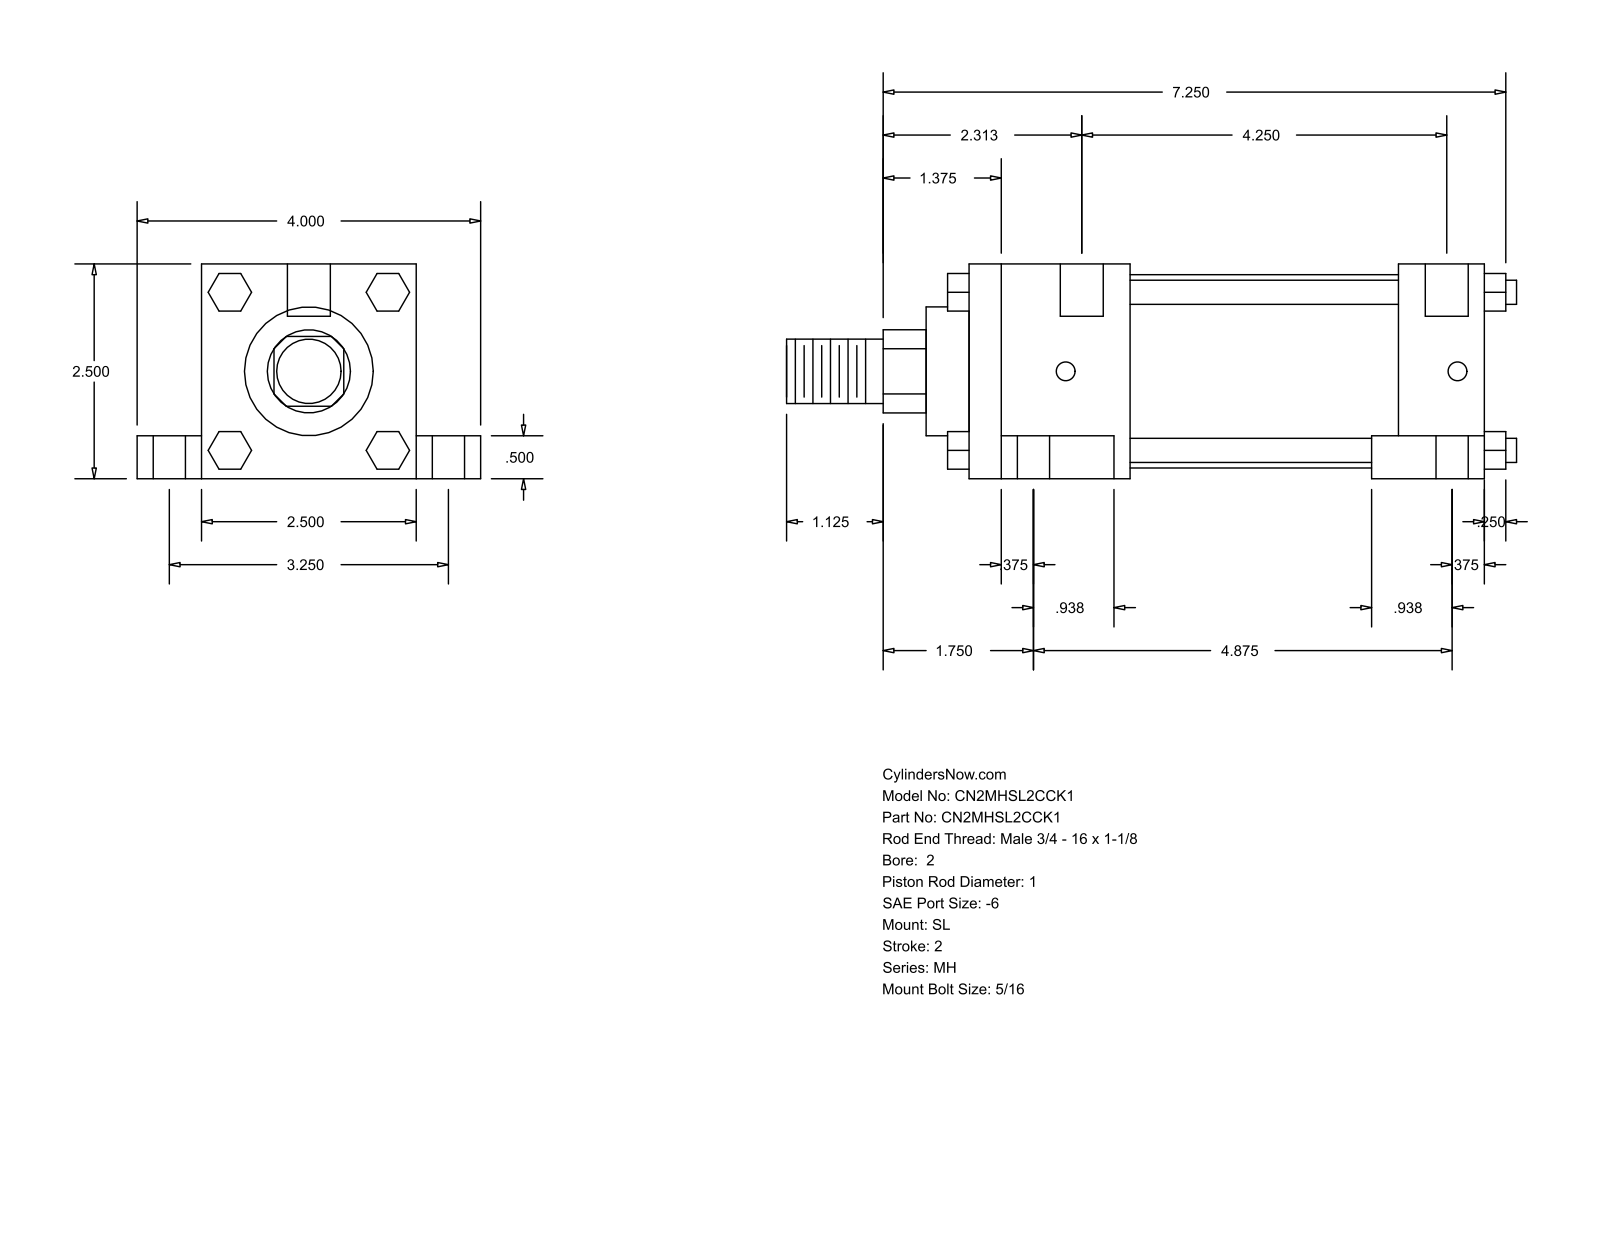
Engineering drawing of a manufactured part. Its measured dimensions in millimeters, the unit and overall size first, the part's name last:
Units: millimetres
Overall size (bounding box): 215.9 × 101.6 × 63.5
Round holes (diameter × count): ⌀5.56 ×4, ⌀9.53 ×4, ⌀15.88 ×4, ⌀12.7 ×2
Round bosses / shafts (diameter × count): ⌀7.14 ×4, ⌀57.15 ×1, ⌀38.1 ×1, ⌀25.4 ×1, ⌀19.05 ×1
Partial cylindrical surfaces — rounded edges, fillets, slot ends (radius × count): R12.29 ×1
Main face-to-face distances: 63.5, 152.4, 12.7, 19.05, 50.8, 82.55, 25.4, 127, 47.63, 79.37
Hole centre spacings: 41.3, 42.36, 43.67, 82.54, 115.88, 117.06, 121.52, 123.83
Bodies: 0 solids, 148 faces (112 planar, 36 cylindrical, 0 other)
Part name (STEP PRODUCT): MH_SL__0200_1
STEP written by: GSSL Pune (CONFIG_CONTROL_DESIGN)
